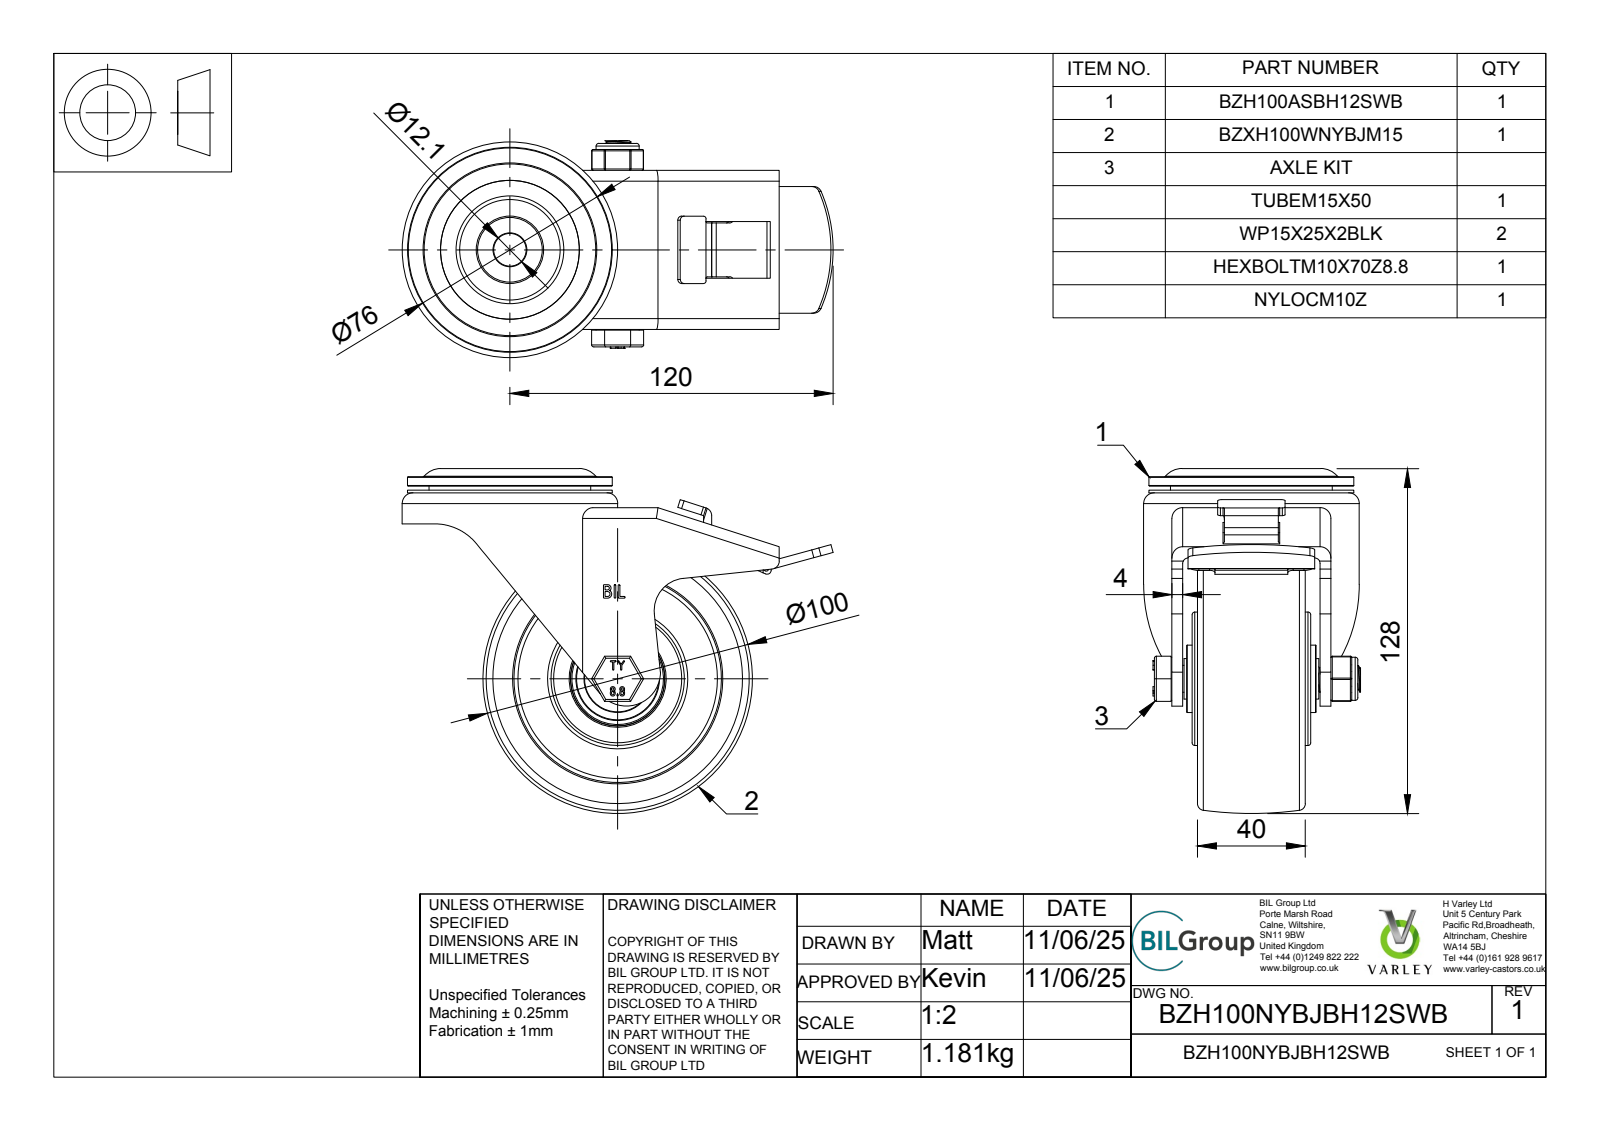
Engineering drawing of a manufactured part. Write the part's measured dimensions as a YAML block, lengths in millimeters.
part_name: "BZH100NYBJBH12SWB v3; BZH100ASBH12SWB v1; ZINC PLATED, PRESSED STEEL TOP PLATE; ZINC PLATED, PRESSED STEEL FORKS (+7 more)"
step_written_by: "Autodesk Translation Framework v14.10.0.0 (AUTOMOTIVE_DESIGN)"
units: millimeters
bodies: {solids: 40, faces: 1237, planar: 554, cylindrical: 245, other: 438}
overall_size: [160, 128, 80.5]
volume: 344669
surface_area: 142654
round_holes:
  - {diameter: 32, count: 2}
  - {diameter: 8, count: 1}
  - {diameter: 10, count: 1}
  - {diameter: 10.25, count: 1}
  - {diameter: 10.5, count: 1}
  - {diameter: 12, count: 1}
  - {diameter: 12.1, count: 1}
  - {diameter: 15, count: 1}
  - {diameter: 15.75, count: 1}
  - {diameter: 17, count: 1}
  - {diameter: 20, count: 1}
  - {diameter: 22.5, count: 1}
round_bosses_or_shafts:
  - {diameter: 25, count: 2}
  - {diameter: 80, count: 1}
  - {diameter: 76, count: 1}
  - {diameter: 60, count: 1}
  - {diameter: 49.5, count: 1}
  - {diameter: 39, count: 1}
  - {diameter: 30.5, count: 1}
  - {diameter: 30.12, count: 1}
partial_cylinders:
  - {radius: 0.5, count: 20}
  - {radius: 1.5, count: 11}
  - {radius: 3, count: 9}
  - {radius: 0.25, count: 8}
  - {radius: 2, count: 8}
  - {radius: 0.75, count: 7}
  - {radius: 4, count: 6}
  - {radius: 2.5, count: 3}
face_to_face_distances: [4, 1, 6.5, 5.5, 9.5, 2.5, 5, 31.5, 19.5, 14]
